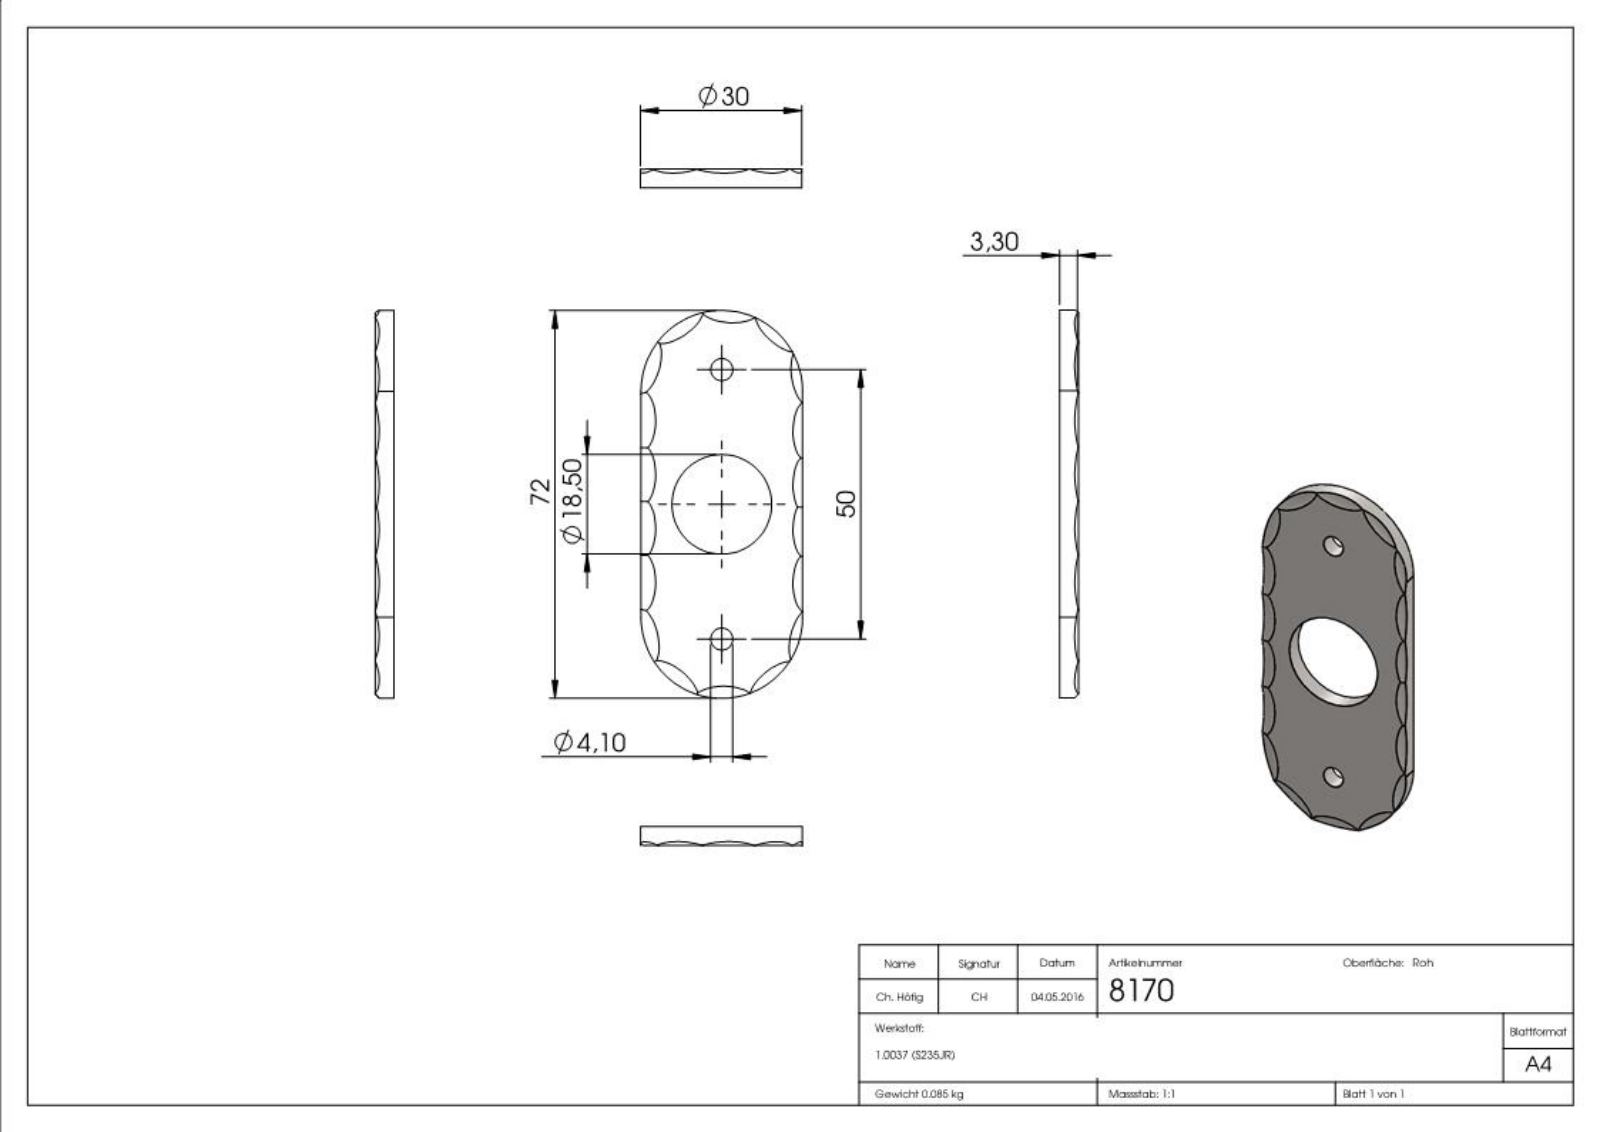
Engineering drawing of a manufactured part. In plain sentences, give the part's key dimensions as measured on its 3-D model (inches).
The part is named "8170". Its 3-D file was written by "SolidWorks 2015 (CONFIG_CONTROL_DESIGN)". It is 1 solid with 631 faces: 109 planar, 138 cylindrical and 384 other. Overall it measures 2.835 by 1.181 by 0.138 inches. Its volume is 0.334 cubic inches and its surface area 6.378 square inches. Round holes: 2 of diameter 0.161, 1 of diameter 0.728. Partial cylindrical surfaces (rounded edges, fillets, slot ends): 16 of radius 0.394, 8 of radius 0.039, 7 of radius 0.455, 3 of radius 0.455, 2 of radius 0.591. The main face-to-face distances are 0.138, 1.181, 0.134, 0.07, 0.03, 0.135, 0.206, 0.048, 0.253, 0.106. The hole center spacings are 0.984, 1.969.
